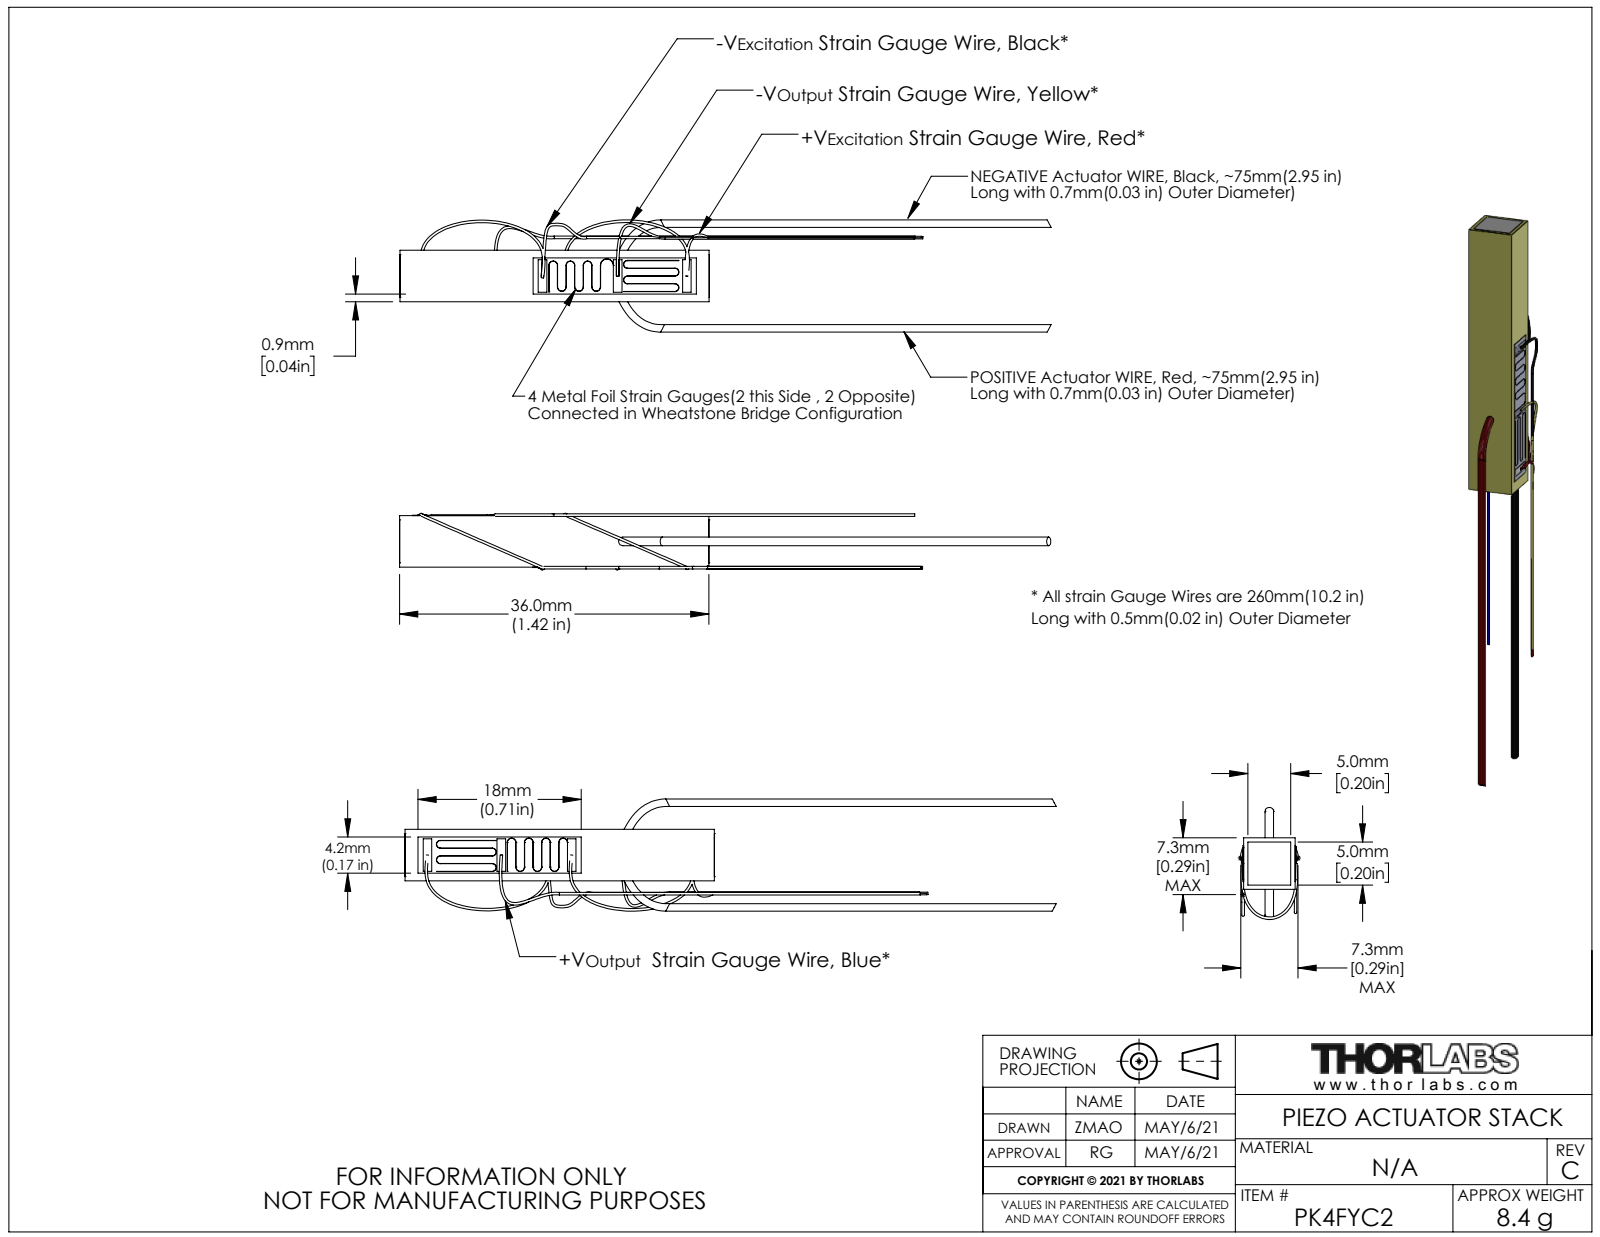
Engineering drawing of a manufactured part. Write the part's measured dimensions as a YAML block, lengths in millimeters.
part_name: "CTN009957-E0W"
step_written_by: "SolidWorks 2018 (AUTOMOTIVE_DESIGN)"
units: millimeters
bodies: {solids: 12, faces: 298, planar: 94, cylindrical: 51, other: 153}
overall_size: [75.81, 13.07, 6.7]
volume: 1388
surface_area: 1817
face_to_face_distances: [6, 6.05, 6.1, 36.01, 36.02, 36, 0.9, 5.1, 4.2, 2.1]
